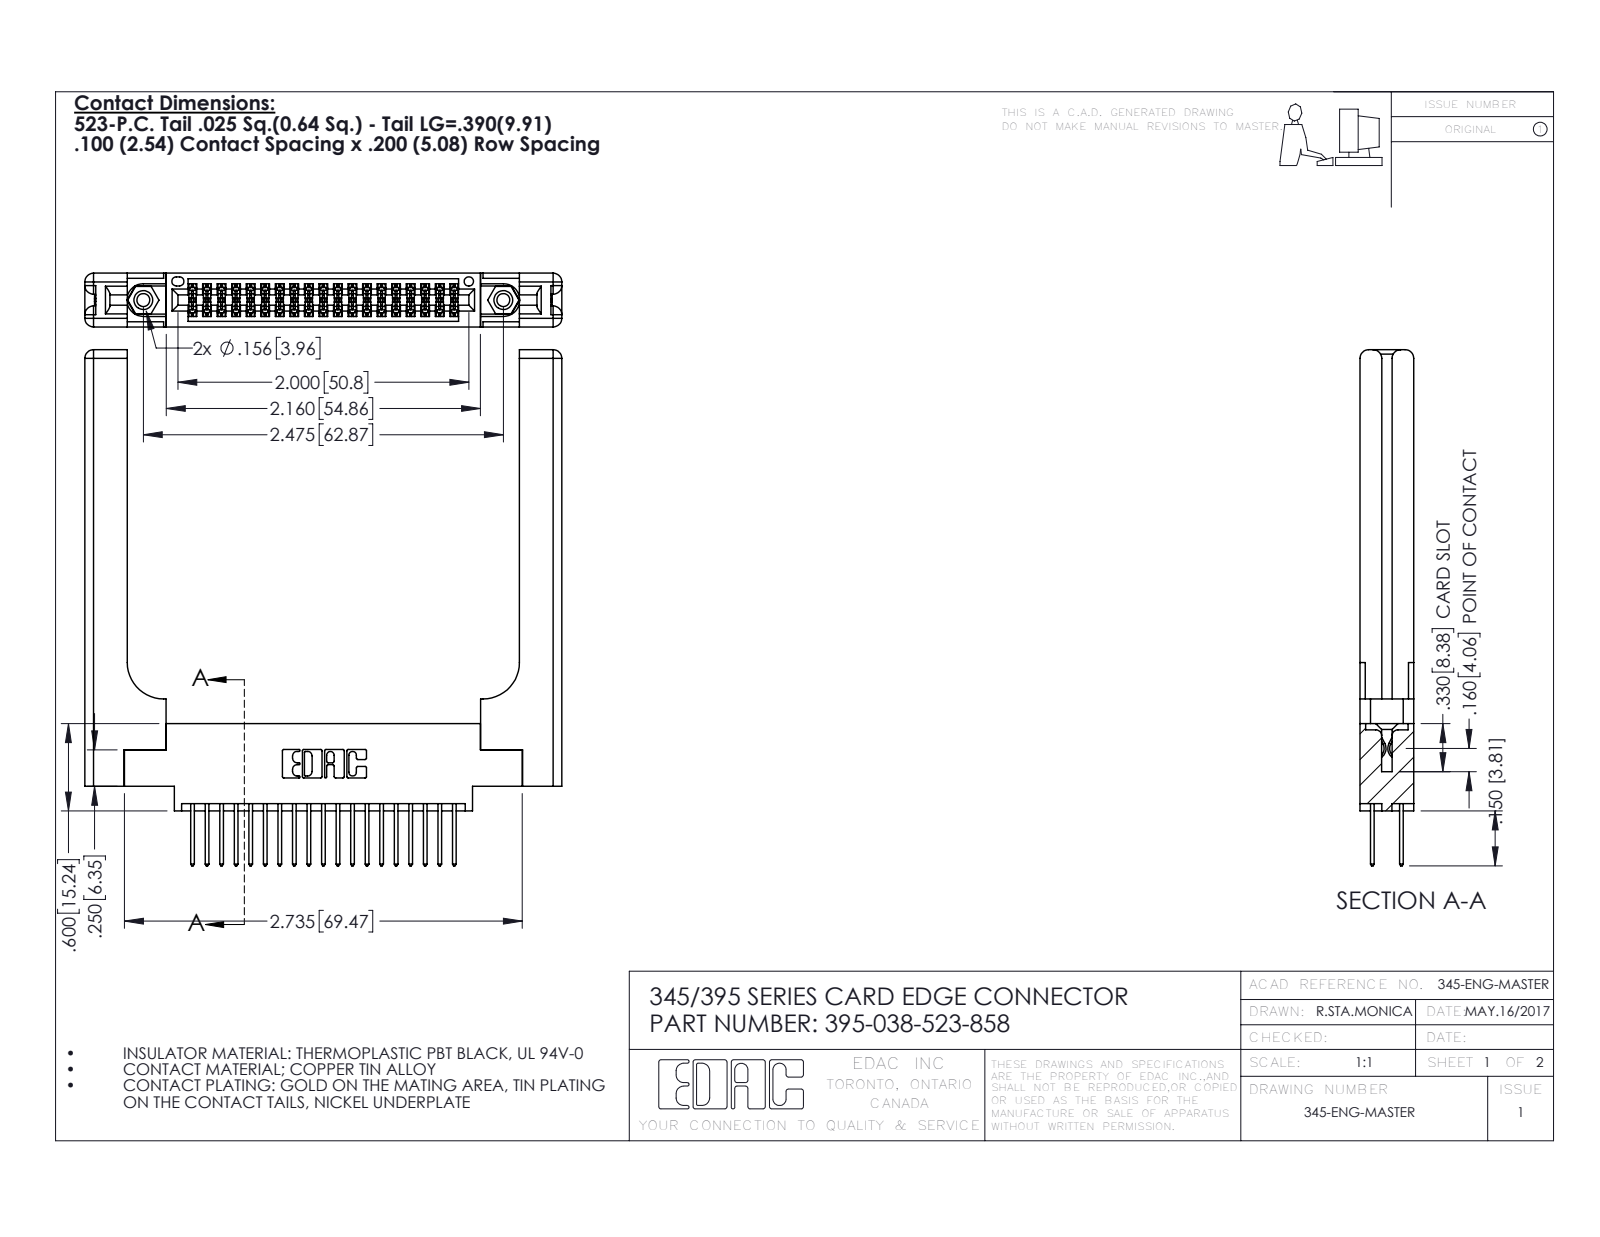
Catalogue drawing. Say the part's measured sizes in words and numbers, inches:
The part is named "395-038-523-858; 345-250-001_345-250-001-102; 345-220-058_345-220-058; 345 Part_0.170 Offset - 0.156 Dia-TH (+1 more)". Its 3-D file was written by "SolidWorks 2016 (CONFIG_CONTROL_DESIGN)". It is 43 solids with 2286 faces: 1486 planar, 740 cylindrical and 60 other. Overall it measures 3.547 by 3.279 by 0.37 inches. Its volume is 0.996 cubic inches and its surface area 25.88 square inches. Round holes: 2 of diameter 0.089, 2 of diameter 0.125, 2 of diameter 0.156, 1 of diameter 0.064. Round bosses or shafts: 2 of diameter 0.155. Partial cylindrical surfaces (rounded edges, fillets, slot ends): 57 of radius 0.006, 38 of radius 0.01, 22 of radius 0.01, 16 of radius 0.06, 6 of radius 0.007, 6 of radius 0.031, 3 of radius 0.026, 2 of radius 0.014. The main face-to-face distances are 0.37, 0.072, 0.298, 0.098, 0.272, 0.025, 0.2, 0.15, 0.148, 0.077. The hole center spacings are 0.27, 2.241, 2.475.
